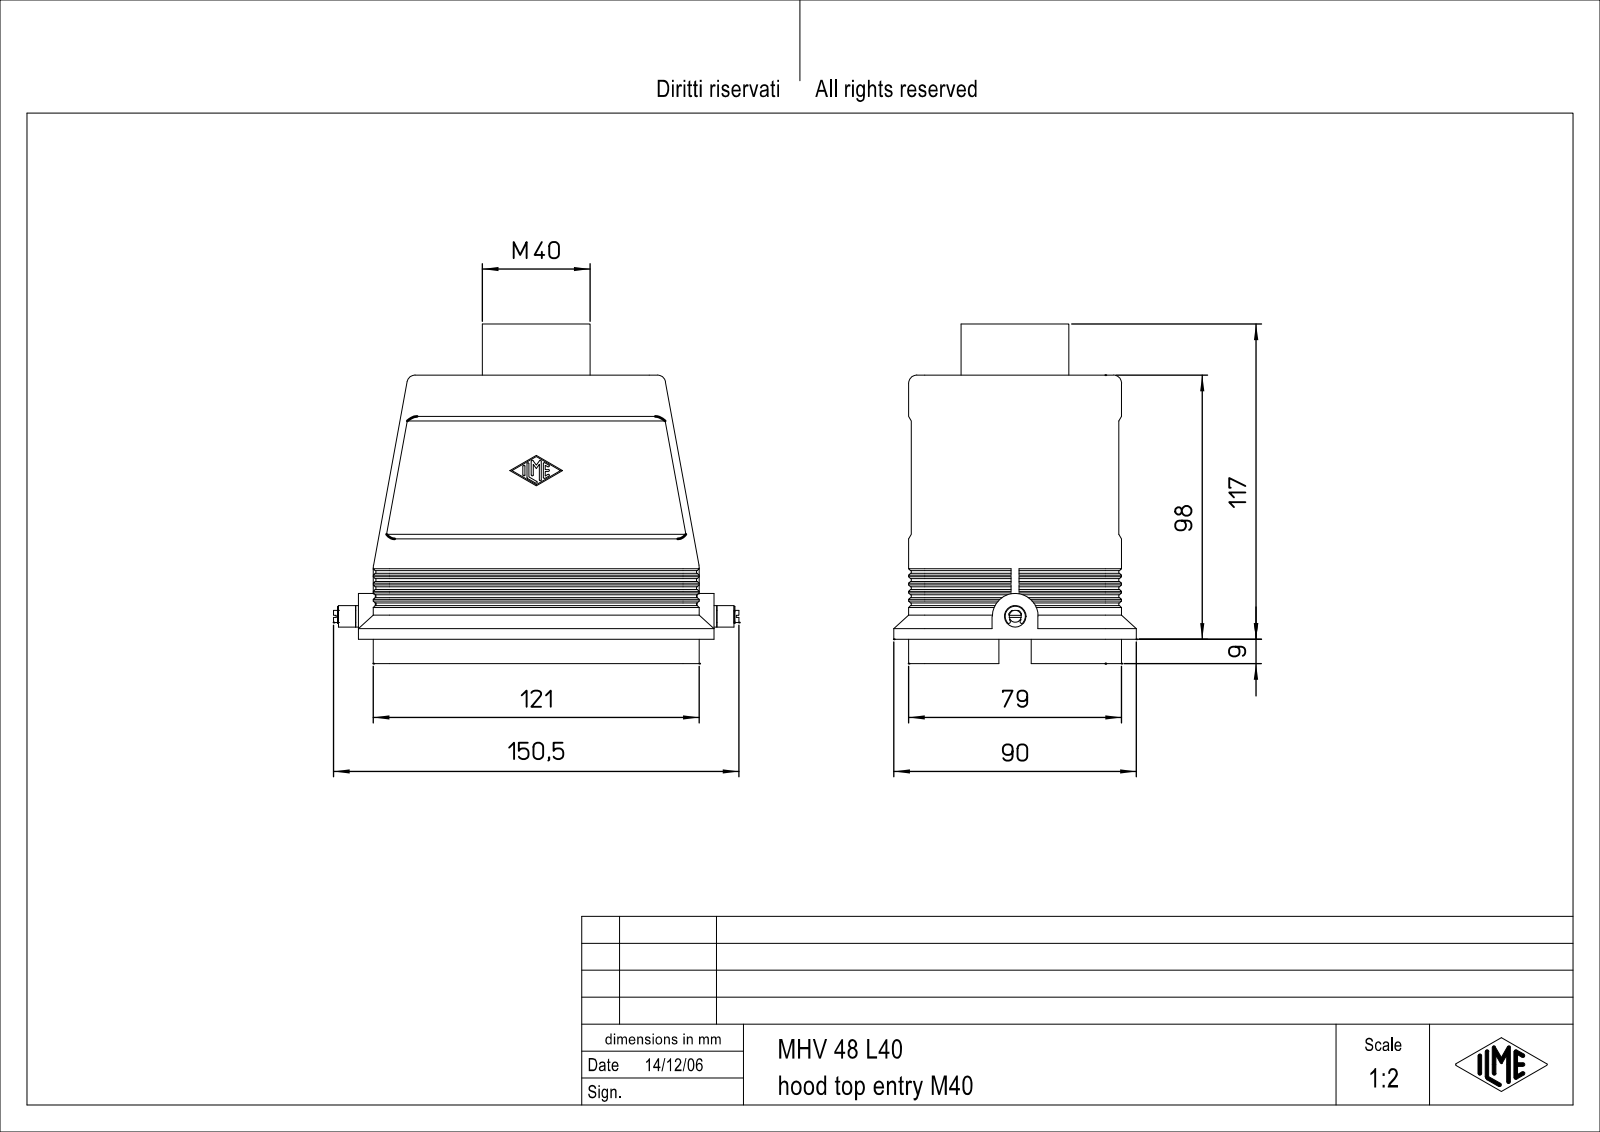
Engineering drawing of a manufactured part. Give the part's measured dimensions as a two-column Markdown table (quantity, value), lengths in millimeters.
| quantity | value |
| --- | --- |
| part name | CH_MH Tüllengehäuse Verschluss für 1 Bügel 104_62 Teil 2 |
| STEP written by | Autodesk Inventor 7 (AUTOMOTIVE_DESIGN) |
| units | millimeters |
| bodies | 1 solid, 686 faces (250 planar, 185 cylindrical, 251 other) |
| overall size | 150.5 × 127 × 90 |
| volume | 237 873 mm³ |
| surface area | 111 244 mm² |
| round holes (diameter × count) | 2.46 × 4, 3.5 × 4, 38 × 1, 40 × 1, 56 × 1 |
| round bosses / shafts (diameter × count) | 55 × 1, 49 × 1, 43 × 1, 8 × 1, 6 × 1, 4.5 × 1, 3.5 × 1 |
| partial cylindrical surfaces (radius × count) | 0.38 × 14, 2 × 12, 6 × 10, 0.5 × 4, 3 × 4, 11.5 × 4, 0.95 × 3, 0.62 × 2 |
| main face-to-face distances | 3.5, 72, 75.5, 109, 1, 2.5, 79, 74.5, 78, 10 |
| hole center spacings | 27, 52.15, 60.54, 104, 107.45 |
